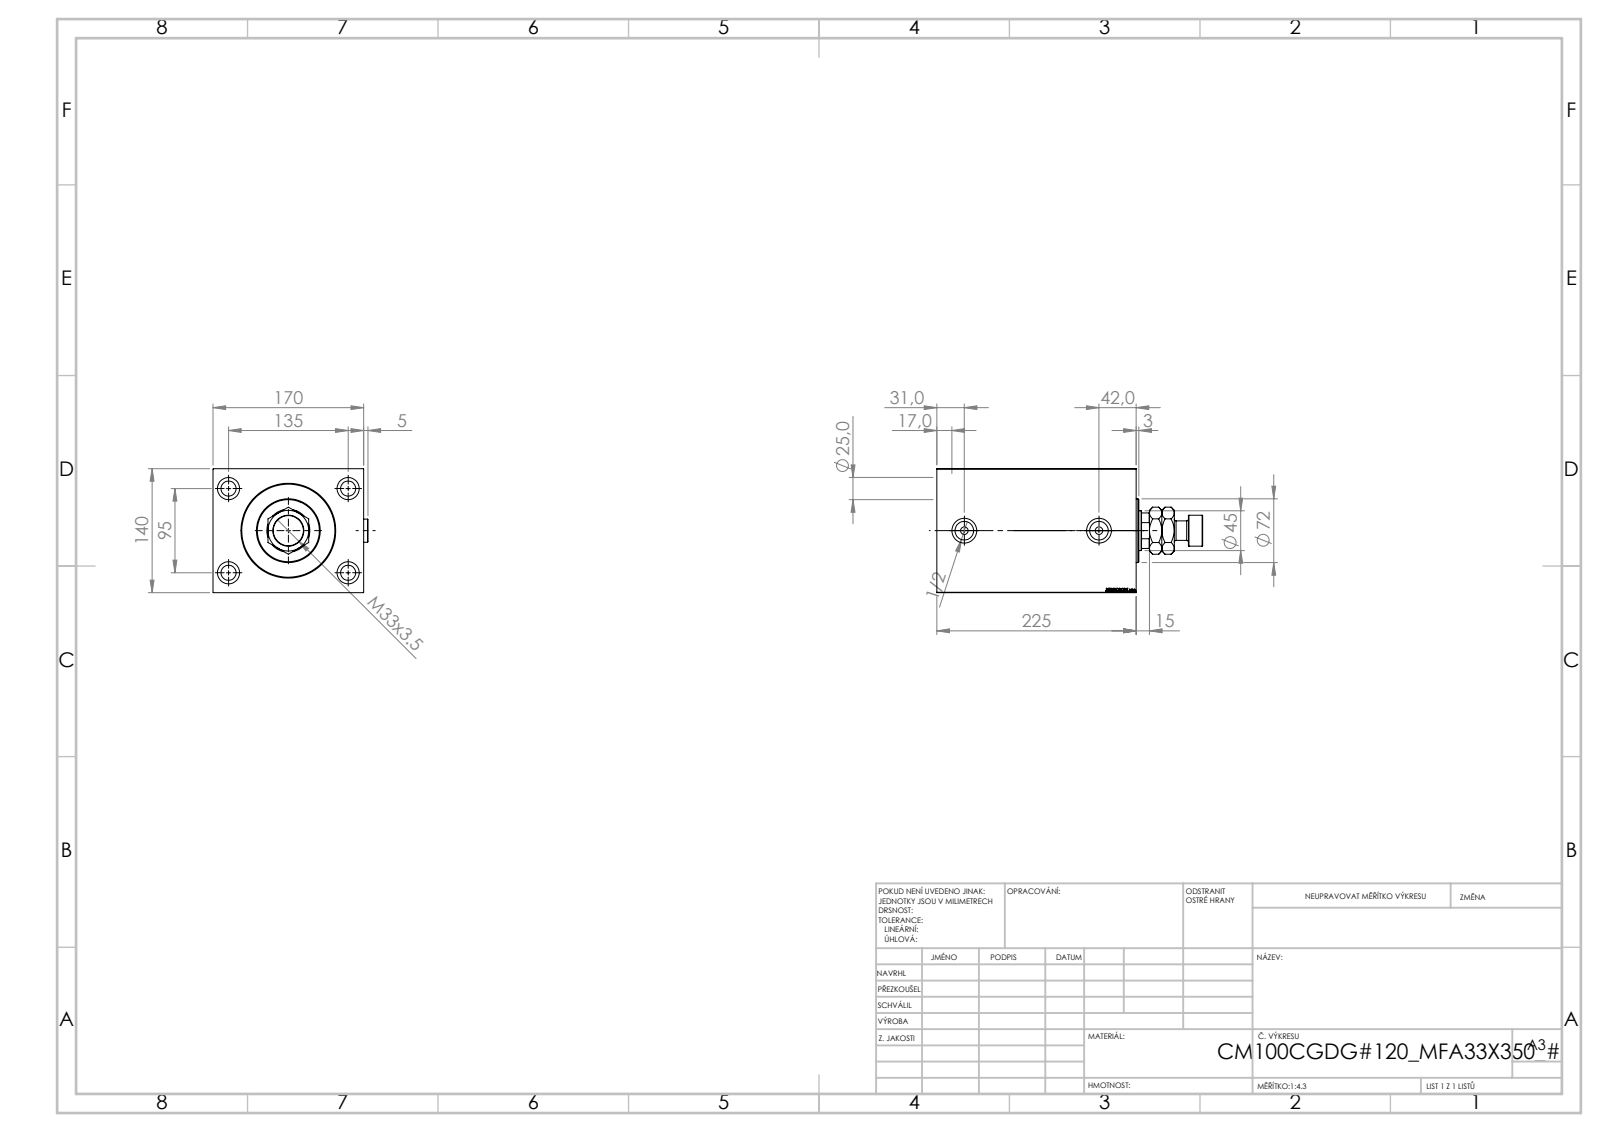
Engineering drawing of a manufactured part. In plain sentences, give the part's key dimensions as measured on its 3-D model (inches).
The part is named "MFA; Zatka_OIL_PORT; V450CM_C_VCP; V450CM_VC_B (+1 more)". Its 3-D file was written by "SolidWorks 2019 (CONFIG_CONTROL_DESIGN)". It is 6 solids with 971 faces: 459 planar, 82 cylindrical and 430 other. Overall it measures 11.811 by 6.886 by 5.512 inches. Its volume is 269.4 cubic inches and its surface area 623.5 square inches. Round holes: 4 of diameter 0.669, 4 of diameter 0.984, 2 of diameter 0.335, 2 of diameter 0.825, 2 of diameter 1.102, 1 of diameter 1.24, 1 of diameter 1.772, 1 of diameter 1.909, 1 of diameter 3.937, 1 of diameter 4.016, 1 of diameter 4.134. Round bosses or shafts: 2 of diameter 1.024, 1 of diameter 2.835, 1 of diameter 1.378, 1 of diameter 0.866. Partial cylindrical surfaces (rounded edges, fillets, slot ends): 1 of radius 0.866. The main face-to-face distances are 5.512, 6.693, 8.858, 7.835, 1.024, 0.591, 8.268, 3.543, 7.244, 2.52. The hole center spacings are 3.25, 3.74, 5.315, 6.499, 5.984.
